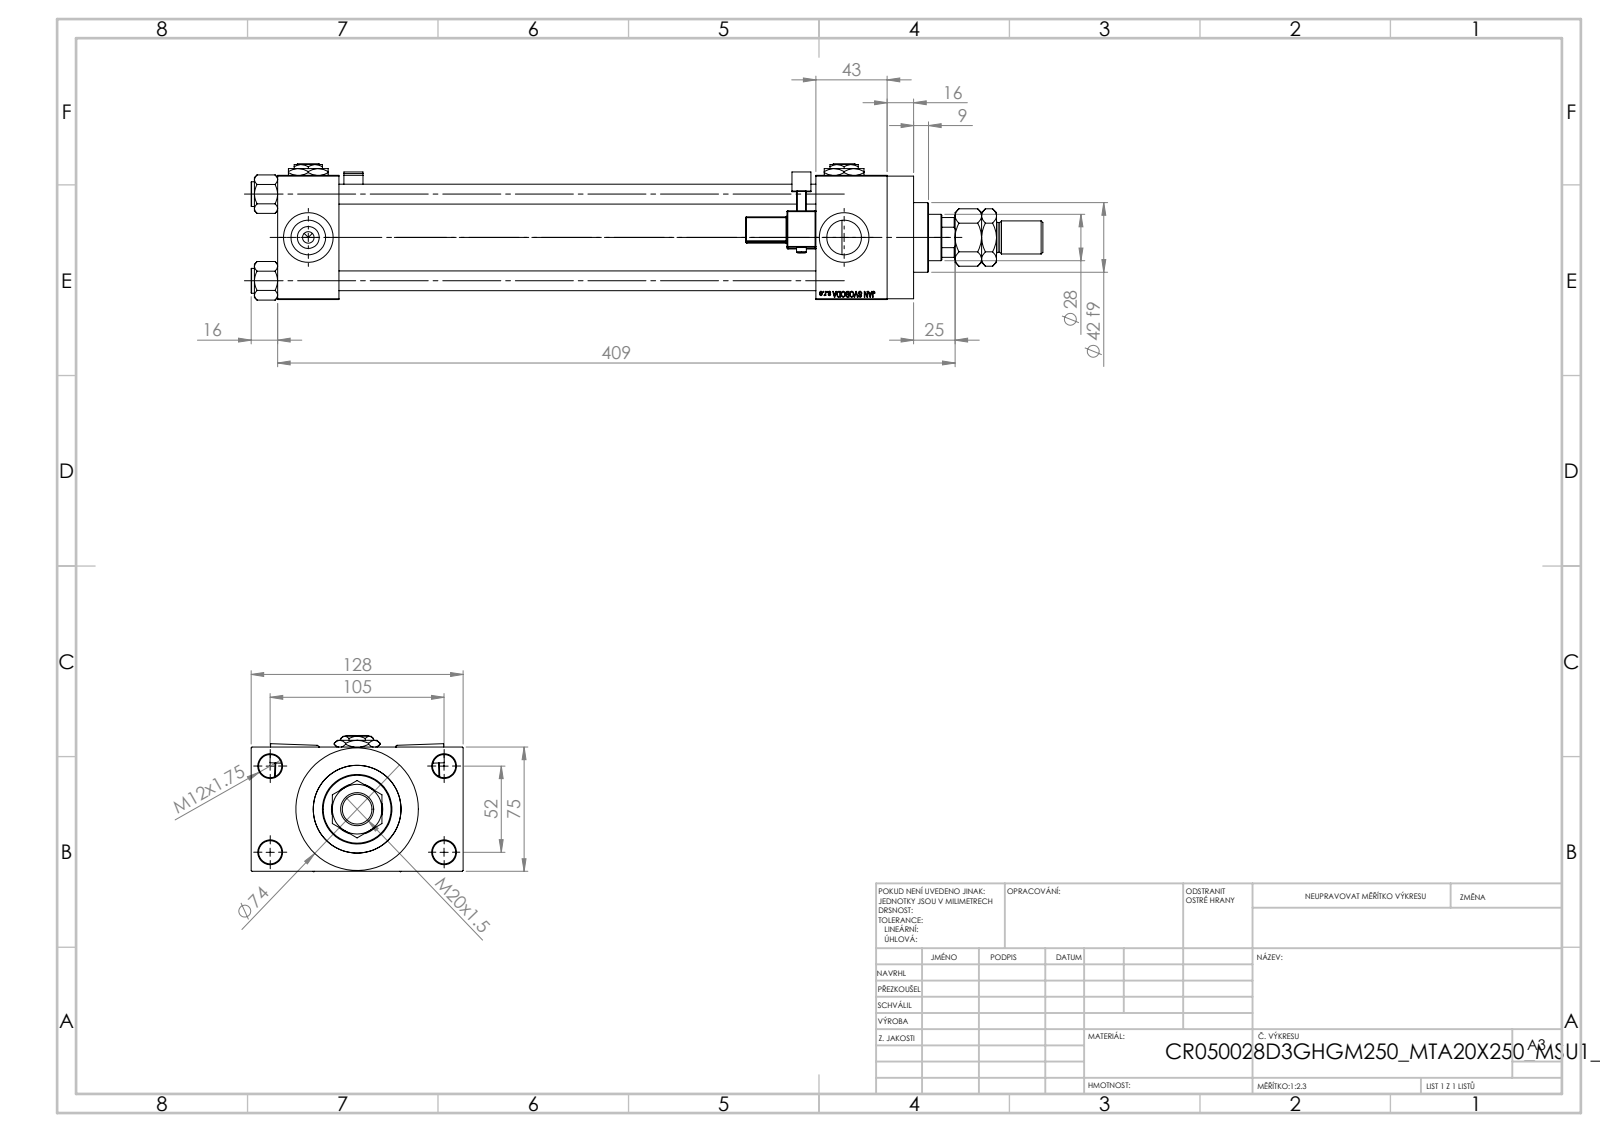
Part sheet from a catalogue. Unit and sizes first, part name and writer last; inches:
Units: inches
Overall size (bounding box): 18.819 × 5.039 × 3.239
Round holes (diameter × count): ⌀0.472 ×4, ⌀0.551 ×4, ⌀0.825 ×4, ⌀1.181 ×4, ⌀0.276 ×3, ⌀0.728 ×1, ⌀1.102 ×1, ⌀1.22 ×1, ⌀1.614 ×1, ⌀1.969 ×1, ⌀2.087 ×1
Round bosses / shafts (diameter × count): ⌀0.591 ×4, ⌀0.236 ×2, ⌀2.913 ×1, ⌀2.205 ×1, ⌀1.654 ×1, ⌀0.787 ×1, ⌀0.709 ×1
Partial cylindrical surfaces — rounded edges, fillets, slot ends (radius × count): R0.02 ×48, R0.039 ×2, R0.098 ×2, R0.157 ×2, R0.531 ×1
Main face-to-face distances: 2.953, 11.339, 1.457, 12.795, 1.043, 3.996, 14.488, 13.031, 1.693, 0.63
Hole centre spacings: 1.037, 1.456, 2.059, 2.3, 2.307, 3.096, 3.715, 2.047
Volume: 75.12 in³ · Surface area: 502.9 in²
Bodies: 16 solids, 1407 faces (618 planar, 163 cylindrical, 626 other)
Part name (STEP PRODUCT): MTA; NUT_M5_D; V215CR_MSU; V215CR_D_TYCINKA (+4 more)
STEP written by: SolidWorks 2019 (CONFIG_CONTROL_DESIGN)
